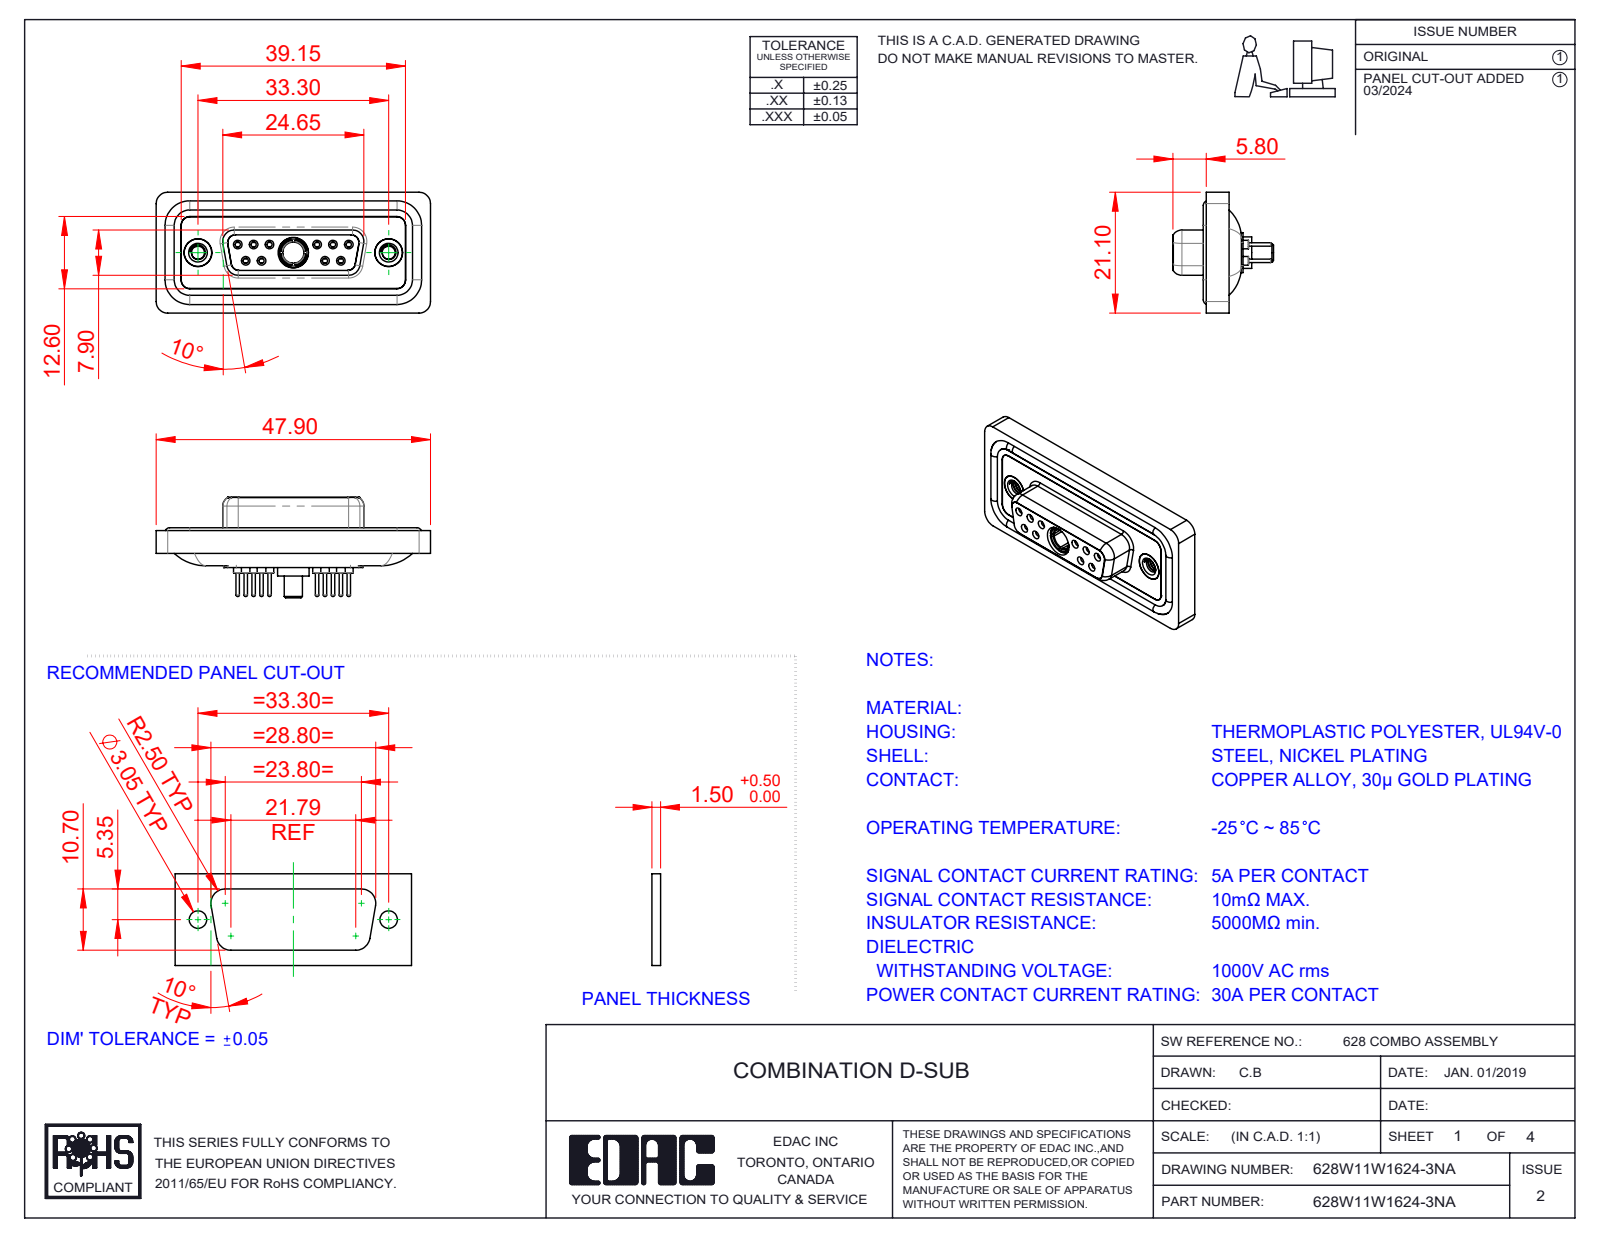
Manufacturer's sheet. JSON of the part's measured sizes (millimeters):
{"part_name": "628Combo Housing_11W1; Power Socket_30A S; 628Combo Shell Rear_15 Contacts; 628Combo Shell Front_15 Contacts (+5 more)", "step_written_by": "SolidWorks 2023 (CONFIG_CONTROL_DESIGN)", "units": "millimeters", "bodies": {"solids": 19, "faces": 1008, "planar": 284, "cylindrical": 403, "other": 321}, "overall_size": [47.9, 21.1, 17.55], "volume_mm3": 6135, "surface_area_mm2": 10034, "round_holes": [[0.9, 10], [1.1, 10], [1.5, 10], [2, 10], [1.7, 6], [1.6, 4], [4.85, 3], [2.26, 2], [4, 2], [4.05, 2], [5, 2], [3.7, 1]], "round_bosses_or_shafts": [[2.2, 10], [1.6, 10], [0.6, 10], [4.95, 2], [4.8, 2], [5.5, 1], [5.2, 1], [4.96, 1]], "partial_cylinders_radius": [[1.5, 22], [2, 20], [1.35, 12], [1.6, 8], [0.25, 4], [0.5, 4], [0.6, 4], [0.65, 4]], "face_to_face_distances": [0.4, 1.6, 1.8, 2.9, 0.5, 1.1, 5.65, 7.45, 6.6, 7.05], "hole_center_spacings": [3.16, 2.77, 13.85, 11.08, 16.62, 5.03, 5.04, 5.54]}
